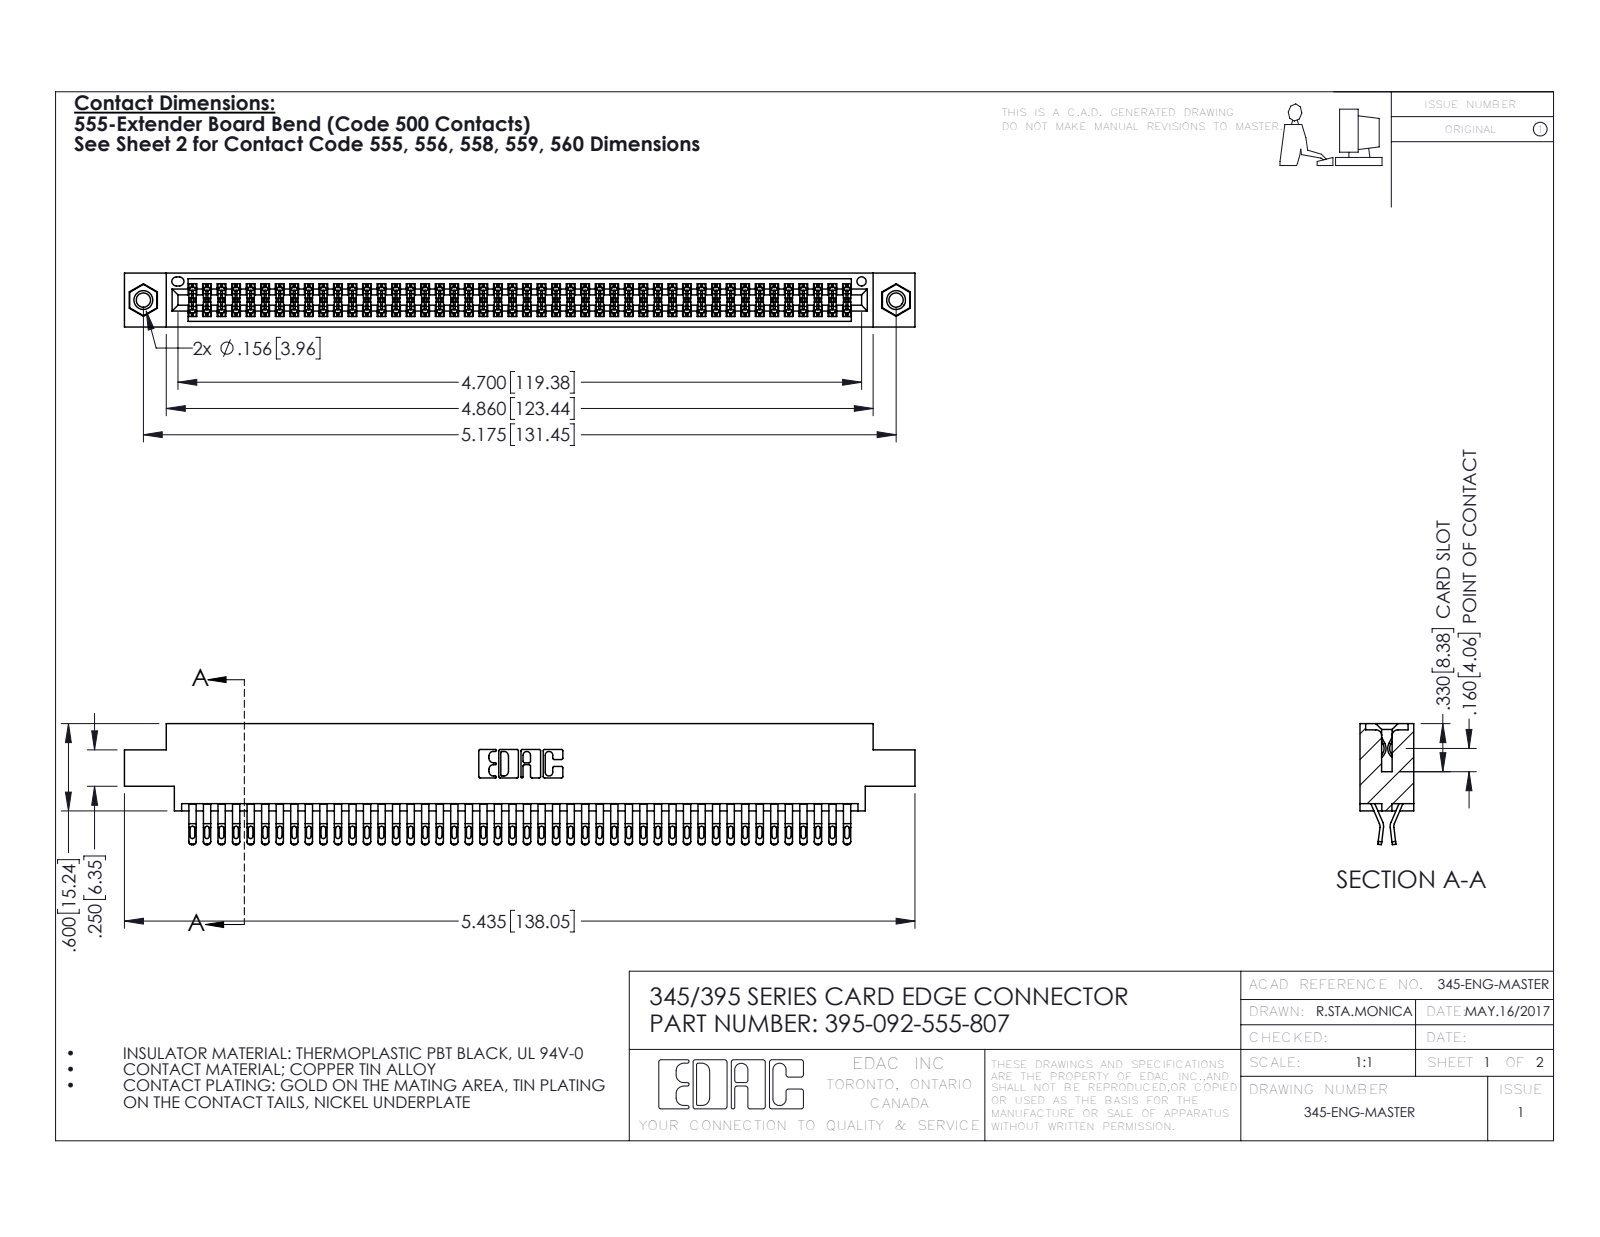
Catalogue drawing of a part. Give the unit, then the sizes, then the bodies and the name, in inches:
Units: inches
Overall size (bounding box): 5.435 × 0.832 × 0.37
Round holes (diameter × count): ⌀0.098 ×2, ⌀0.125 ×2, ⌀0.156 ×2, ⌀0.064 ×1
Round bosses / shafts (diameter × count): ⌀0.155 ×2
Partial cylindrical surfaces — rounded edges, fillets, slot ends (radius × count): R0.016 ×230, R0.02 ×184, R0.006 ×138, R0.01 ×22, R0.007 ×6, R0.031 ×6, R0.026 ×3, R0.01 ×2
Main face-to-face distances: 0.072, 0.298, 0.37, 0.025, 0.2, 0.098, 0.272, 0.225, 0.175, 0.149
Hole centre spacings: 0.27, 4.939, 5.175
Volume: 0.829 in³ · Surface area: 32.96 in²
Bodies: 95 solids, 5342 faces (2968 planar, 2358 cylindrical, 16 other)
Part name (STEP PRODUCT): 345 Part_0.170 Offset - 0.156 Dia-TI; 395-092-555-807; 345-292-001_555 Tail; 345-250-001_345-250-005-103
STEP written by: SolidWorks 2016 (CONFIG_CONTROL_DESIGN)
